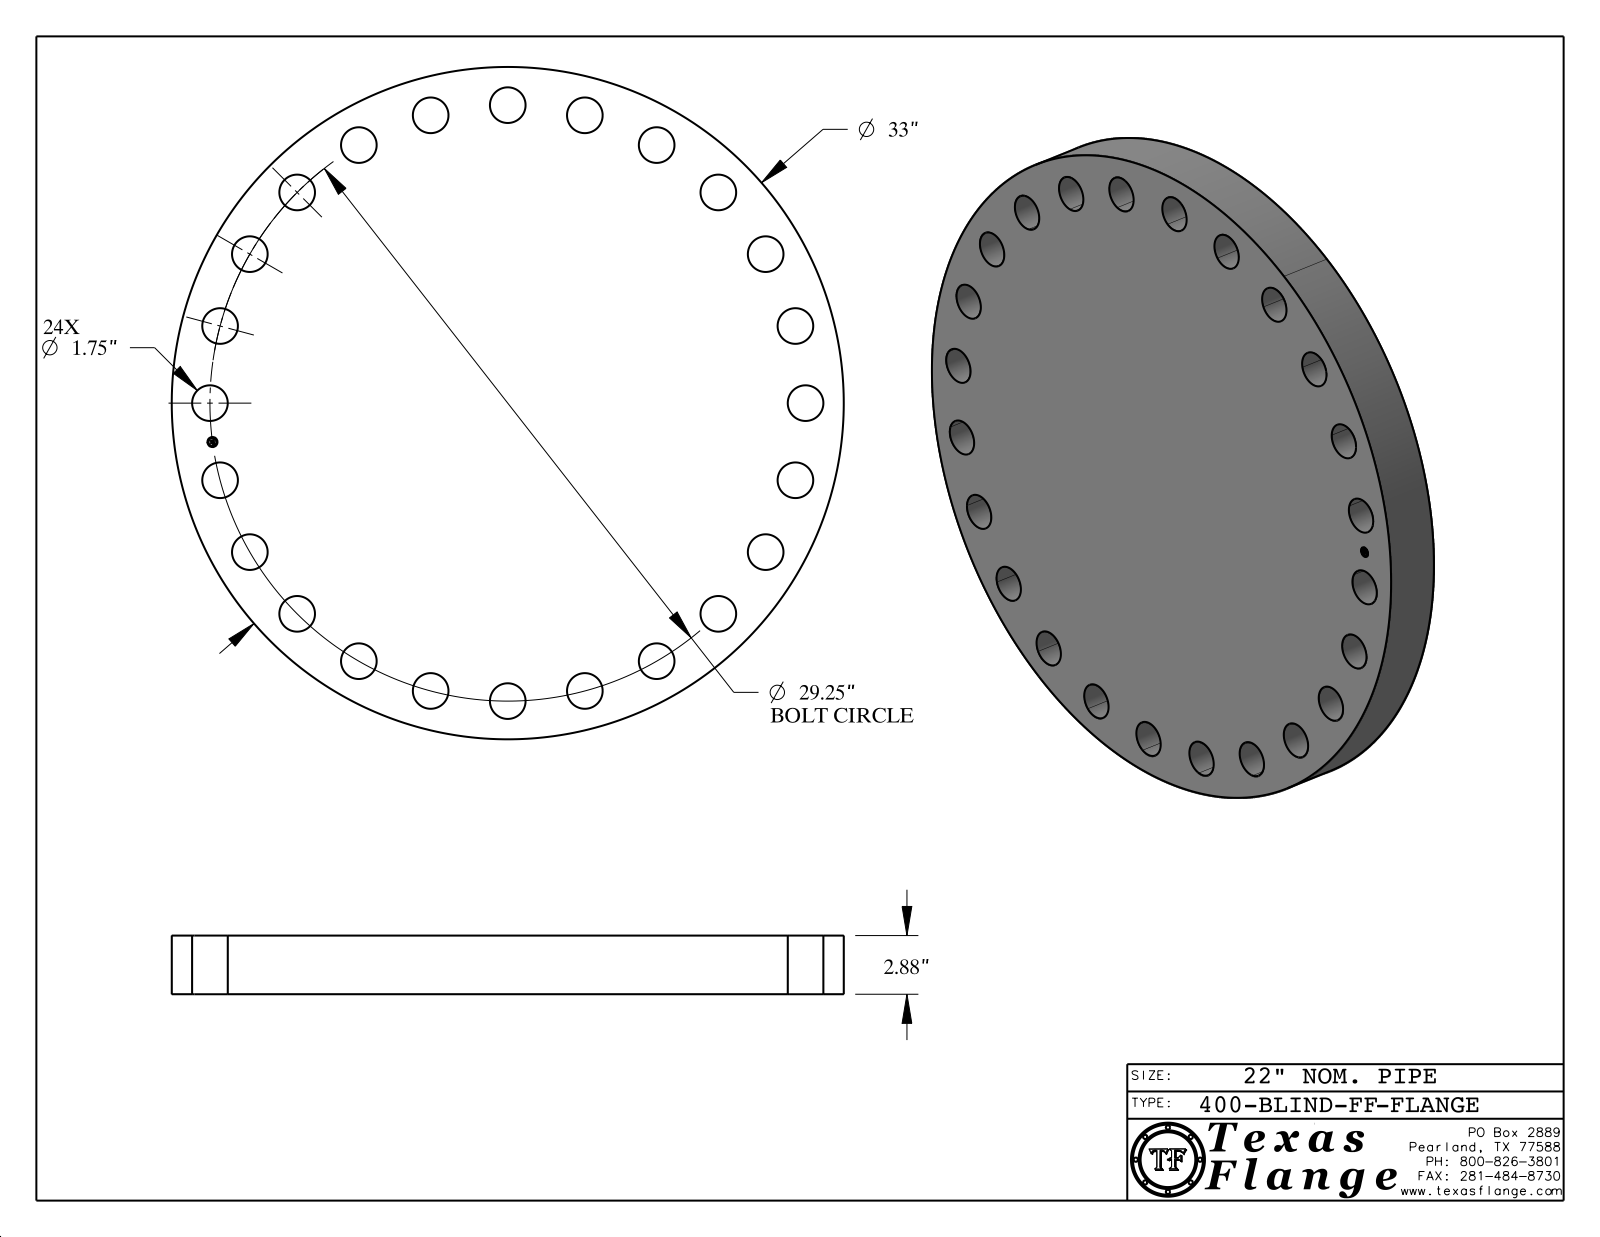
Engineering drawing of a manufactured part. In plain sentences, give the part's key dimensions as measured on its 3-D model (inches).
The part is named "400-BLIND-FF". Its 3-D file was written by "CATIA V5 STEP AP214 (AUTOMOTIVE_DESIGN)". It is 1 solid with 437 faces: 367 planar, 70 cylindrical and 0 other. Overall it measures 33 by 33 by 2.88 inches. Its volume is 2 297 cubic inches and its surface area 2 274 square inches. Round holes: 24 of diameter 1.75, 1 of diameter 0.495. Round bosses or shafts: 8 of diameter 0.03, 1 of diameter 33, 1 of diameter 0.39. The main face-to-face distances are 2.88, 2.865, 0.015, 0.148, 0.145, 0.027, 0.096, 0.123, 0.022, 0.074. The hole center spacings are 27.024, 7.57, 20.683, 3.818, 11.194, 17.806, 23.206, 28.254.
